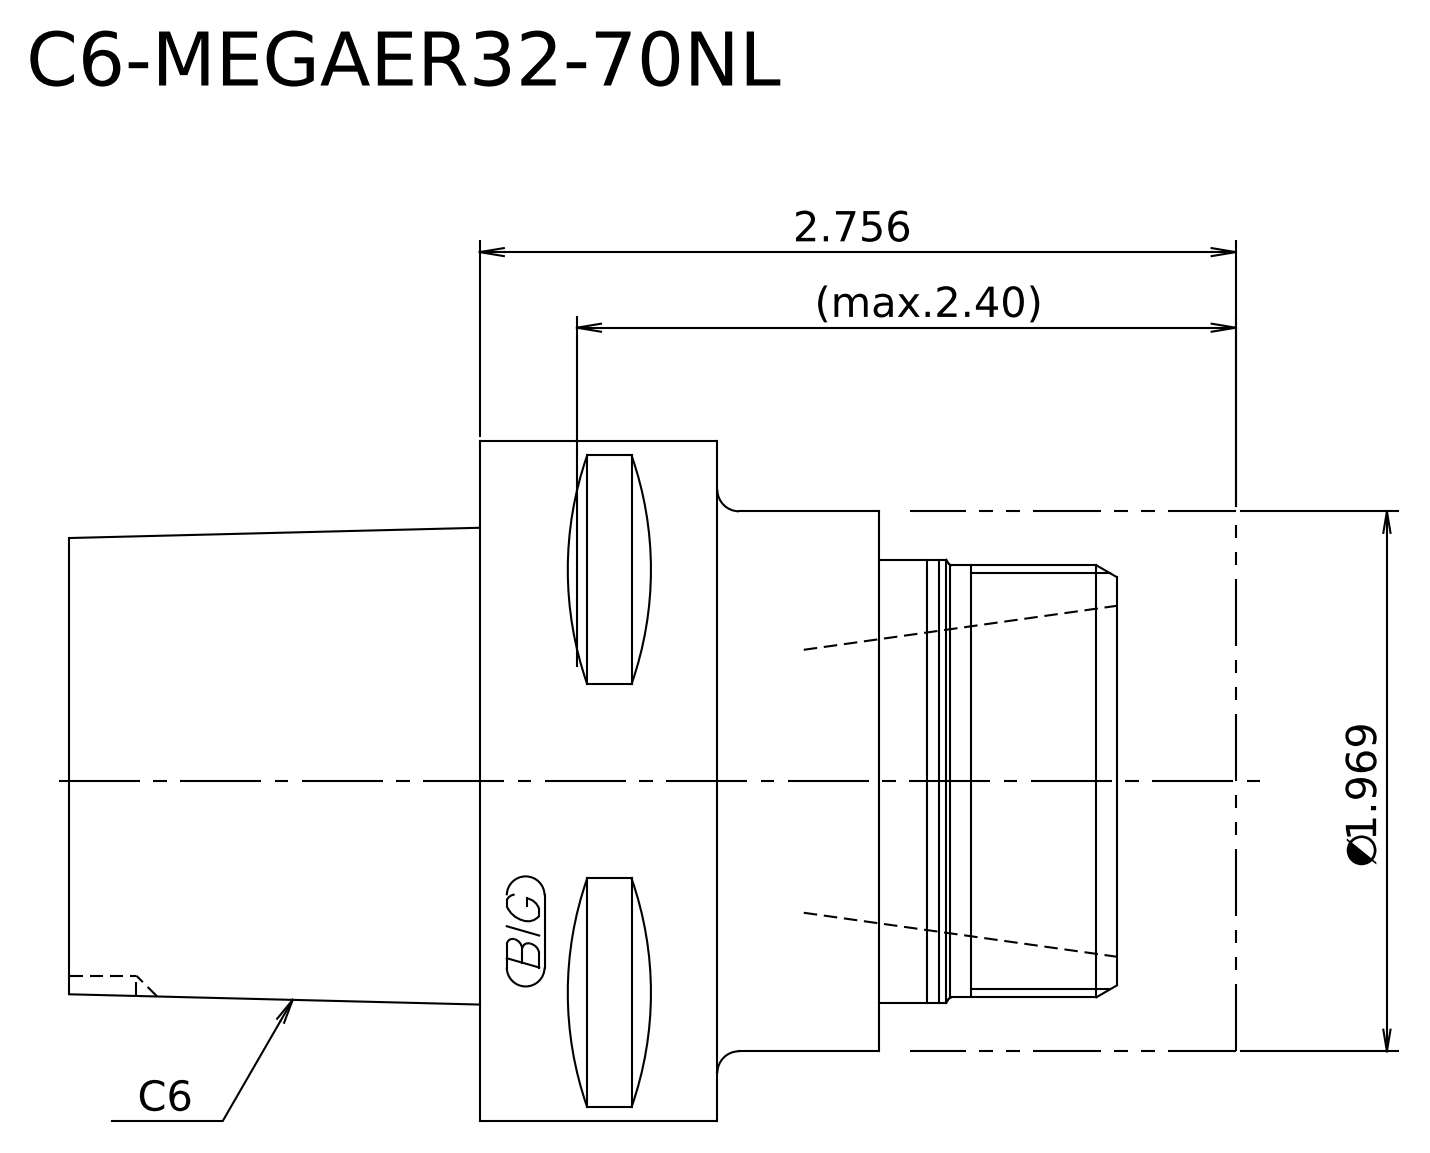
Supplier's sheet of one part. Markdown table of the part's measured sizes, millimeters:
| quantity | value |
| --- | --- |
| STEP written by | Kubotek KeyCreator 2011 V10.0.2 (22737) (automotive_design) |
| units | millimeters |
| bodies | 2 solids, 18 faces (7 planar, 5 cylindrical, 6 other) |
| overall size | 108 × 63 × 63 |
| volume | 240 362 mm³ |
| surface area | 29 119 mm² |
| round bosses / shafts (diameter × count) | 63 × 1, 50 × 1, 41 × 1, 40 × 1 |
| main face-to-face distances | 30.2, 70, 39.8, 22, 37, 108, 77.8, 38, 11, 19.2 |
